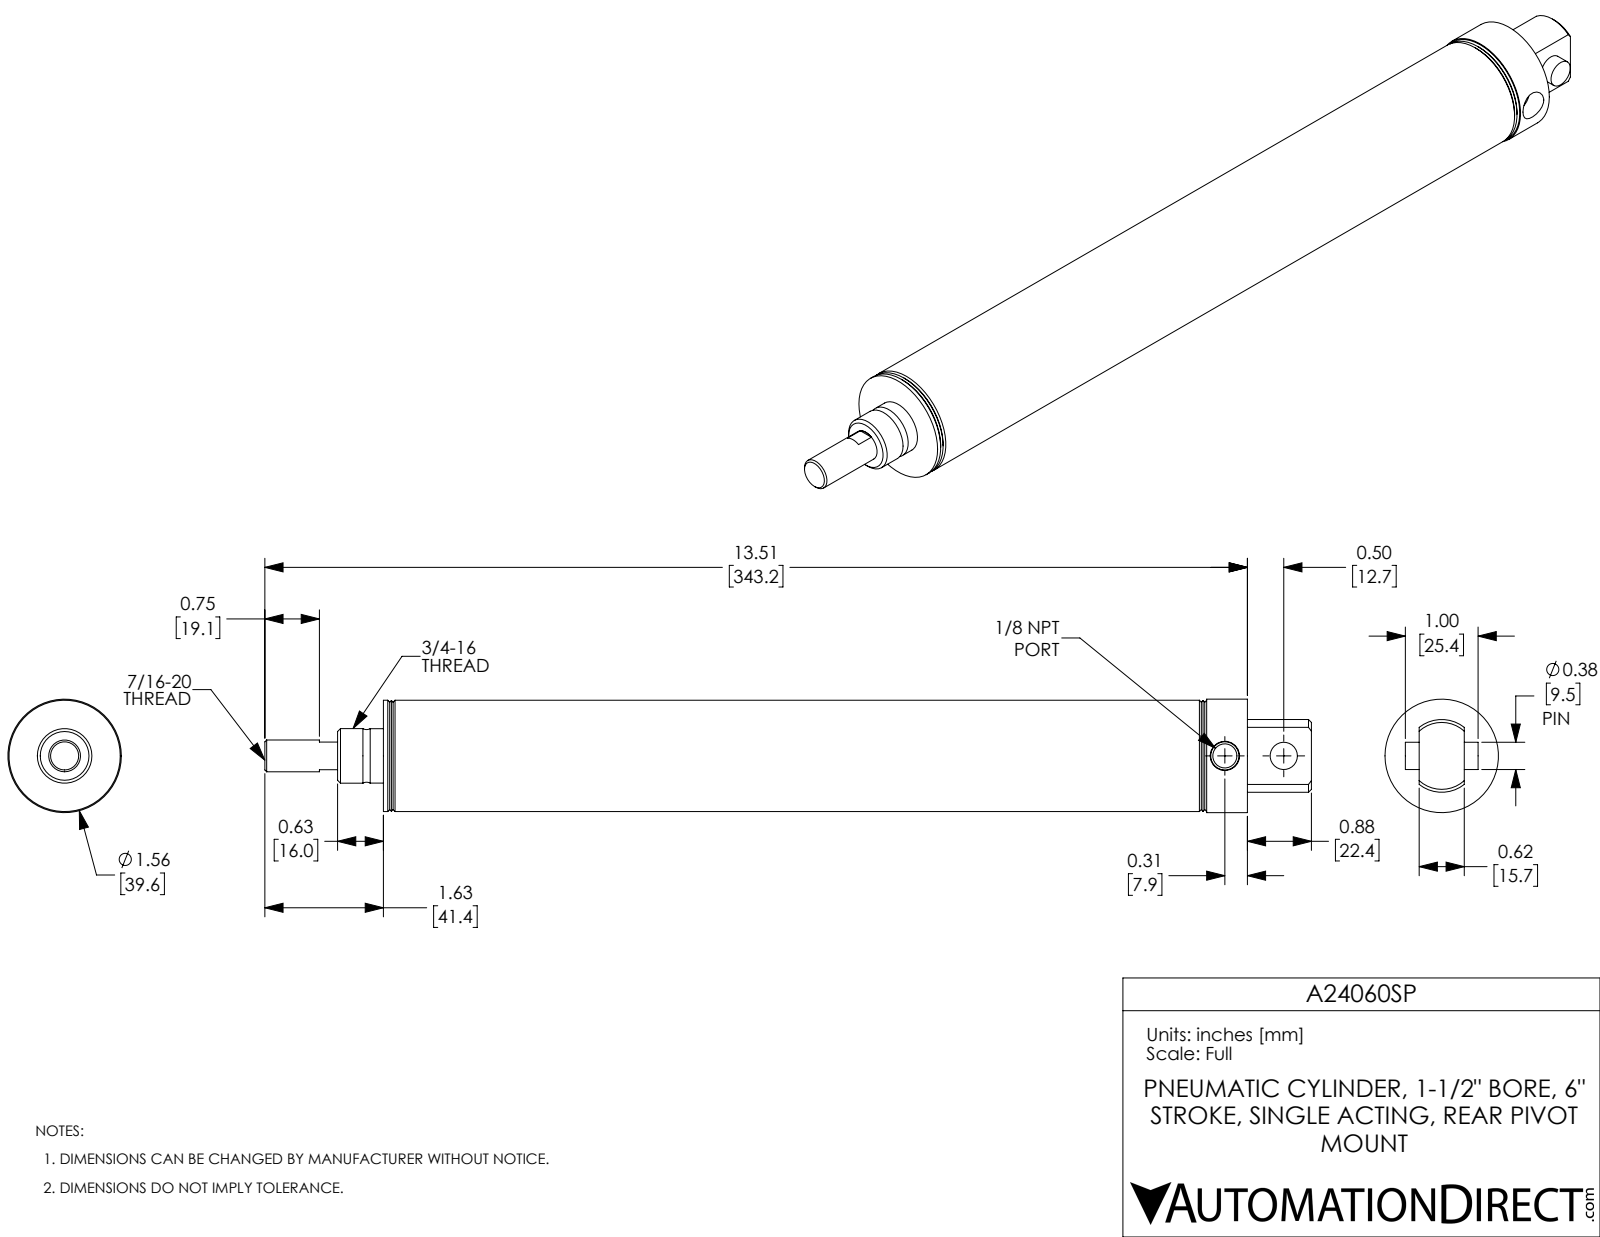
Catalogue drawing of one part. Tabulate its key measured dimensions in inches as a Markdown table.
| quantity | value |
| --- | --- |
| part name | A24060SP-MainBody; A24060SP-Rod; A24060SP-PIN; A24060SP |
| STEP written by | SolidWorks 2017 (AUTOMOTIVE_DESIGN) |
| units | inches |
| bodies | 3 solids, 78 faces (22 planar, 26 cylindrical, 30 other) |
| overall size | 14.39 × 1.56 × 1.56 |
| volume | 13.09 in³ |
| surface area | 125.8 in² |
| round holes (diameter × count) | 0.332 × 1, 0.375 × 1, 0.437 × 1, 1.5 × 1 |
| round bosses / shafts (diameter × count) | 1.56 × 1, 1.53 × 1, 0.75 × 1, 0.747 × 1 |
| partial cylindrical surfaces (radius × count) | 0.5 × 1 |
| main face-to-face distances | 0.5, 6.5, 6, 9.035, 8.535, 2.535, 2.845, 3.345, 9.345, 11.88 |
| hole center spacings | 0.81 |
